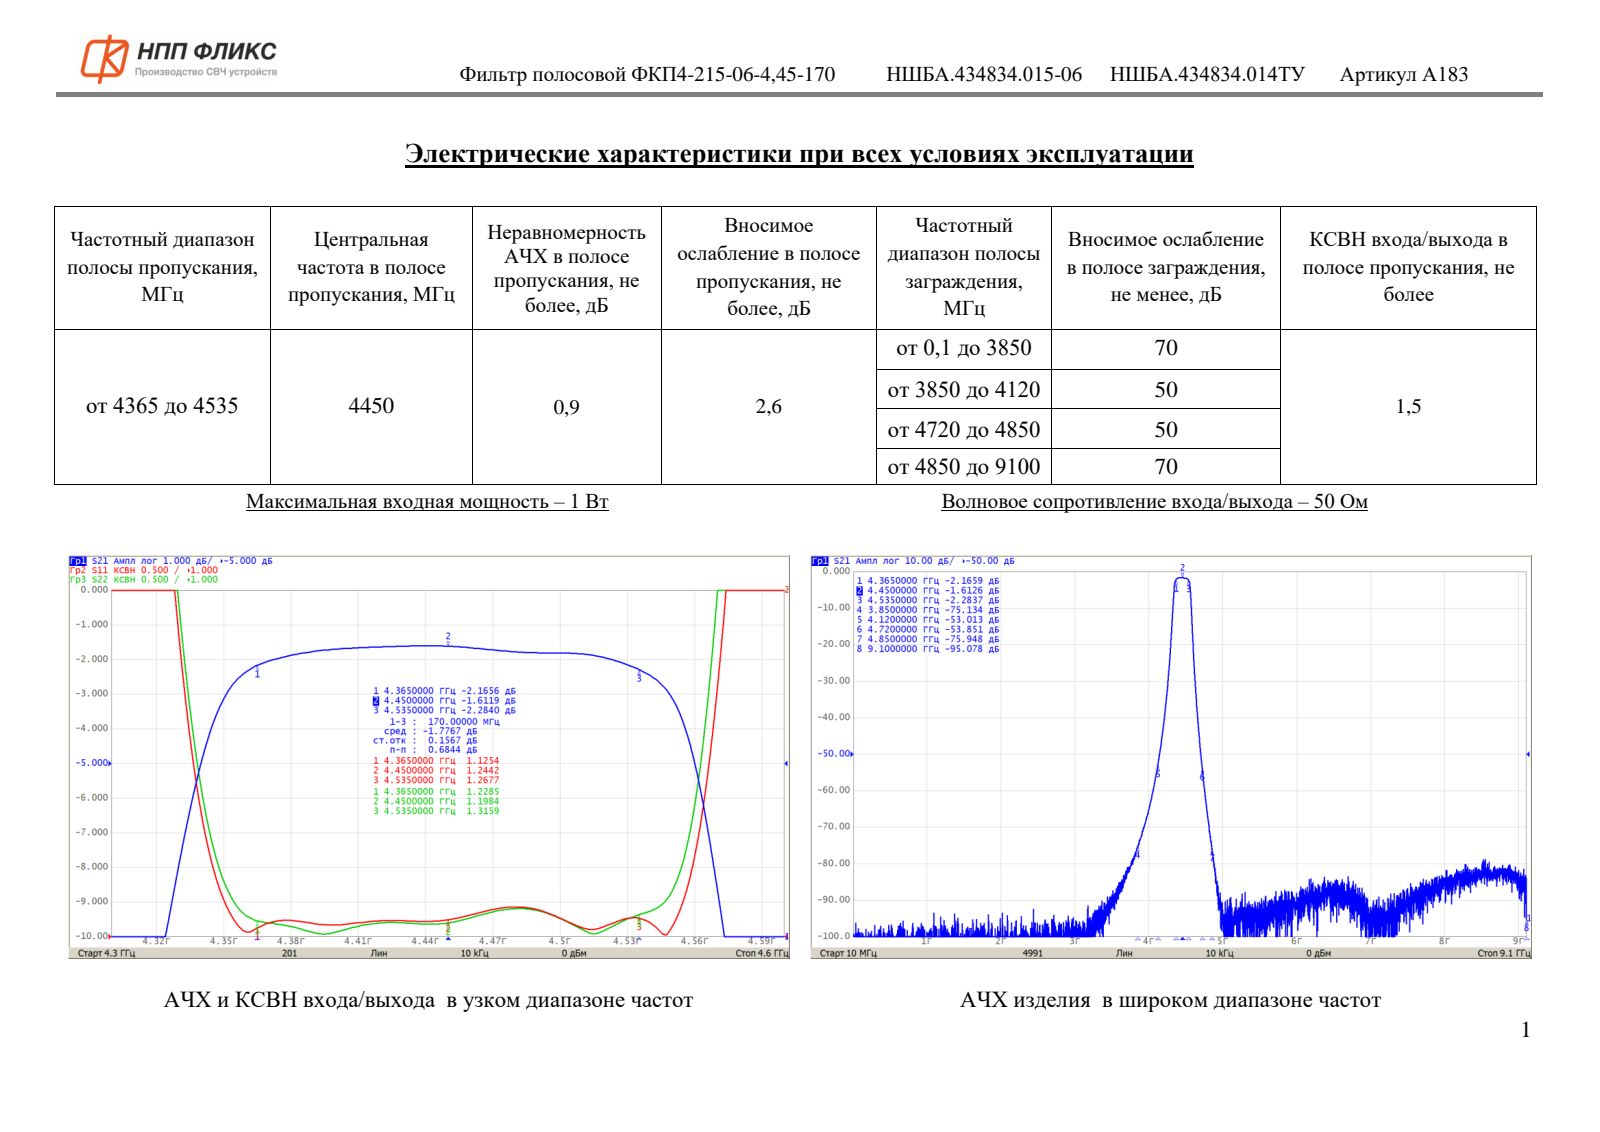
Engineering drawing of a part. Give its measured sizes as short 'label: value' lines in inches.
name: НШБА.434834.015-06_Фильтр ФКП4-215-06-4,45-170
written by: ASCON Math Kernel (CONFIG_CONTROL_DESIGN)
unit: in
bodies: 1 solid, 504 faces (343 planar, 27 cylindrical, 134 other)
size: 0.969 × 0.291 × 0.173
volume: 0.045 in³; area: 1.02 in²
holes: 5× ⌀0.059, 1× ⌀0.037
bosses: 1× ⌀0.034, 1× ⌀0.008
rounds: 4× R0.059, 4× R0.063, 3× R0.008, 1× R0.004, 1× R0.012, 1× R0.014
face distances: 0.171, 0.291, 0.906, 0.173, 0.016, 0.276, 0.017, 0.274, 0.259, 0.014
hole spacings: 0.148, 0.295, 0.443, 0.591
